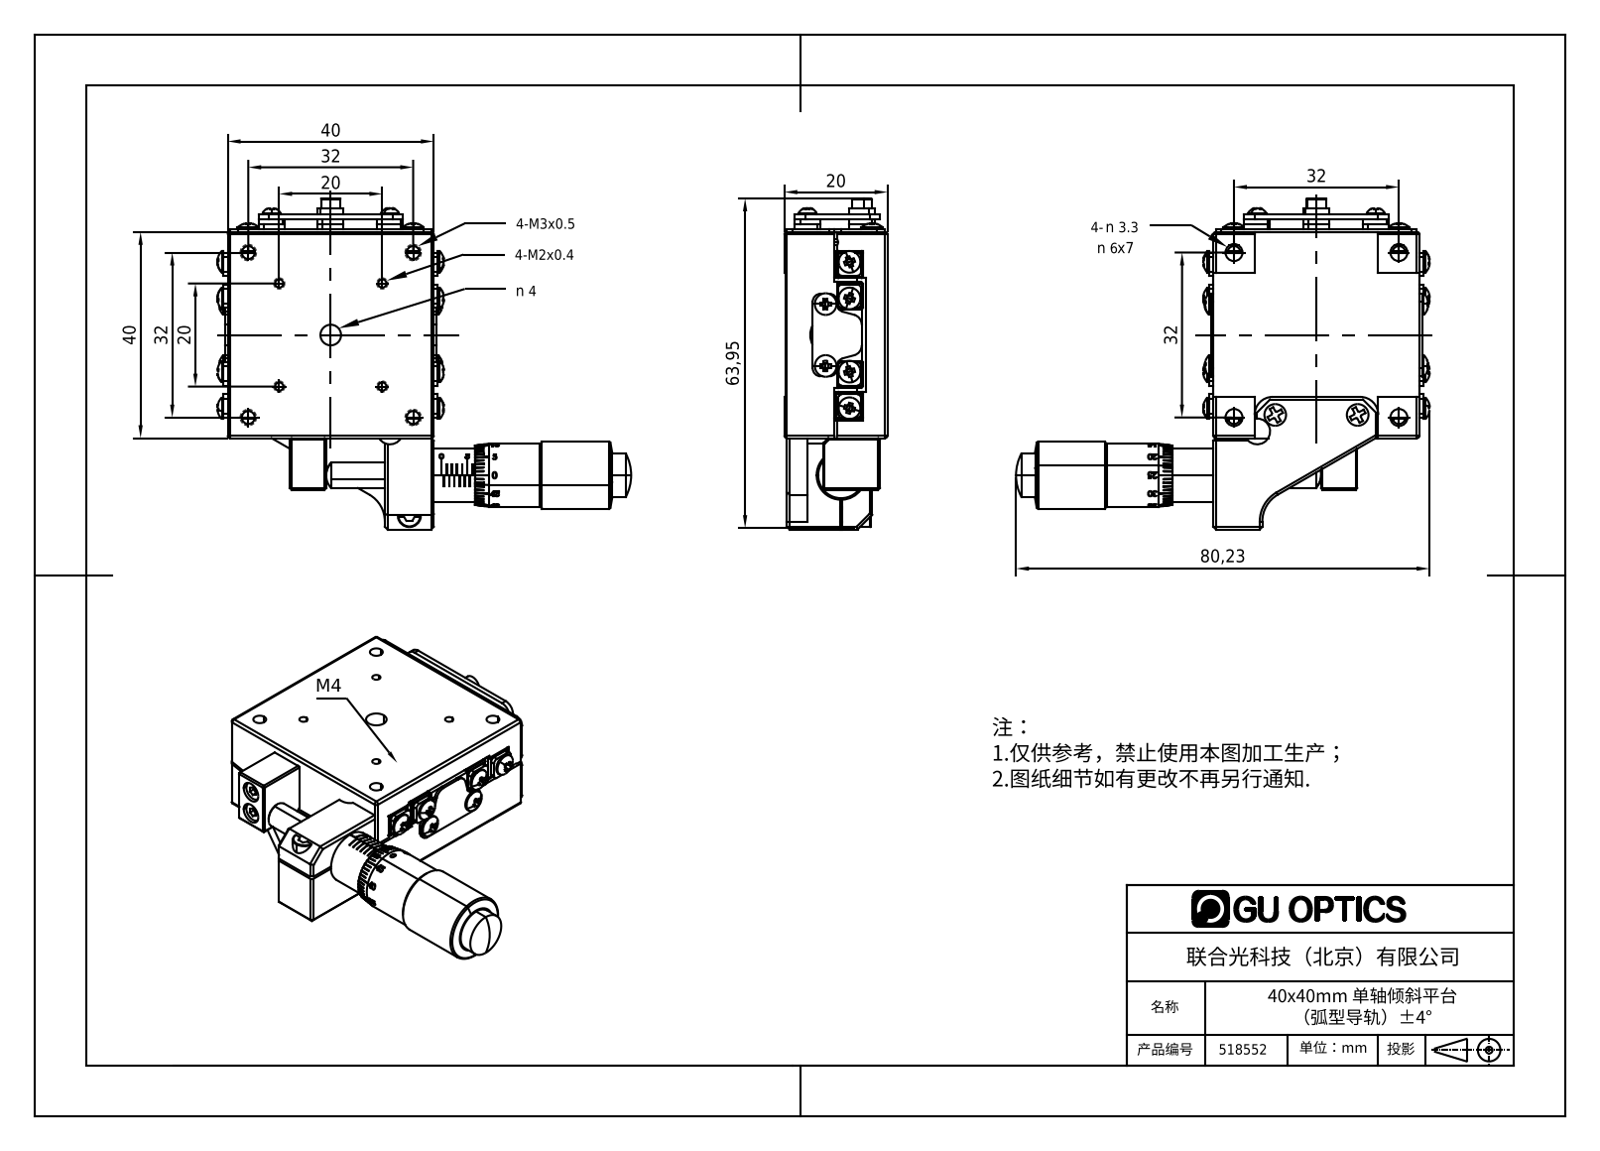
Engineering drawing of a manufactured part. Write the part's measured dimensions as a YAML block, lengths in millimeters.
part_name: "MXG4-80VM"
step_written_by: "SolidWorks 2020 (CONFIG_CONTROL_DESIGN)"
units: millimeters
bodies: {solids: 2, faces: 1428, planar: 956, cylindrical: 289, other: 183}
overall_size: [80.23, 64.2, 20]
volume: 36609
surface_area: 17901
round_holes:
  - {diameter: 1.6, count: 6}
  - {diameter: 2.5, count: 4}
  - {diameter: 3.3, count: 4}
  - {diameter: 6, count: 4}
  - {diameter: 4, count: 3}
  - {diameter: 8, count: 1}
  - {diameter: 9.5, count: 1}
round_bosses_or_shafts:
  - {diameter: 4.2, count: 8}
  - {diameter: 5, count: 4}
  - {diameter: 3.8, count: 3}
  - {diameter: 3.5, count: 2}
  - {diameter: 13, count: 1}
  - {diameter: 12.25, count: 1}
  - {diameter: 10.5, count: 1}
  - {diameter: 9.1, count: 1}
partial_cylinders:
  - {radius: 0.8, count: 16}
  - {radius: 0.5, count: 12}
  - {radius: 1.5, count: 12}
  - {radius: 2, count: 12}
  - {radius: 1, count: 8}
  - {radius: 3.5, count: 2}
  - {radius: 2.25, count: 1}
  - {radius: 2.5, count: 1}
face_to_face_distances: [19.7, 40.5, 3, 40, 0.5, 19.5, 1, 13.7, 0.8, 21.3]
hole_center_spacings: [26.68, 32, 8.49, 14.14, 20, 22.63, 36.77, 28.28]
